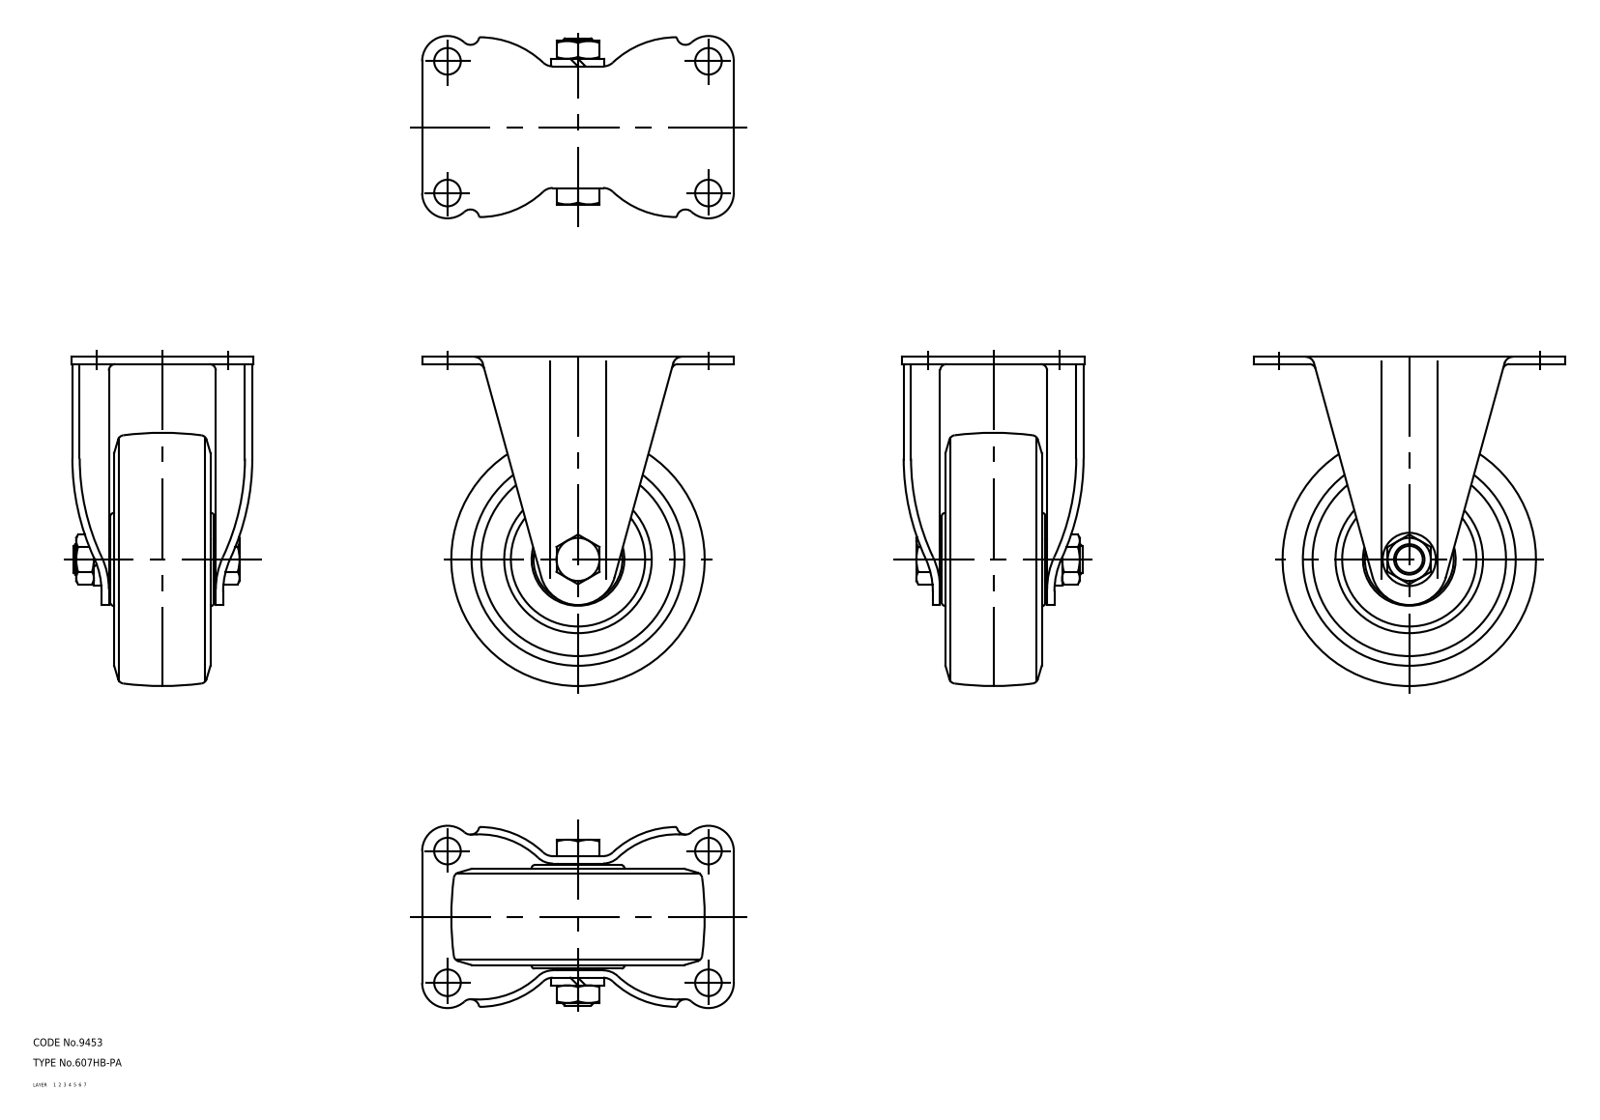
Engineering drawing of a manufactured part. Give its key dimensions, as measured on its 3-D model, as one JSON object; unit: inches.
{"part_name": "67120590; 67120603; 67120616", "step_written_by": "CADfix (AUTOMOTIVE_DESIGN)", "units": "inches", "bodies": {"solids": 3, "faces": 174, "planar": 0, "cylindrical": 0, "other": 174}, "overall_size": [5.118, 4.843, 2.835], "volume_in3": 19.48, "surface_area_in2": 110.1}
